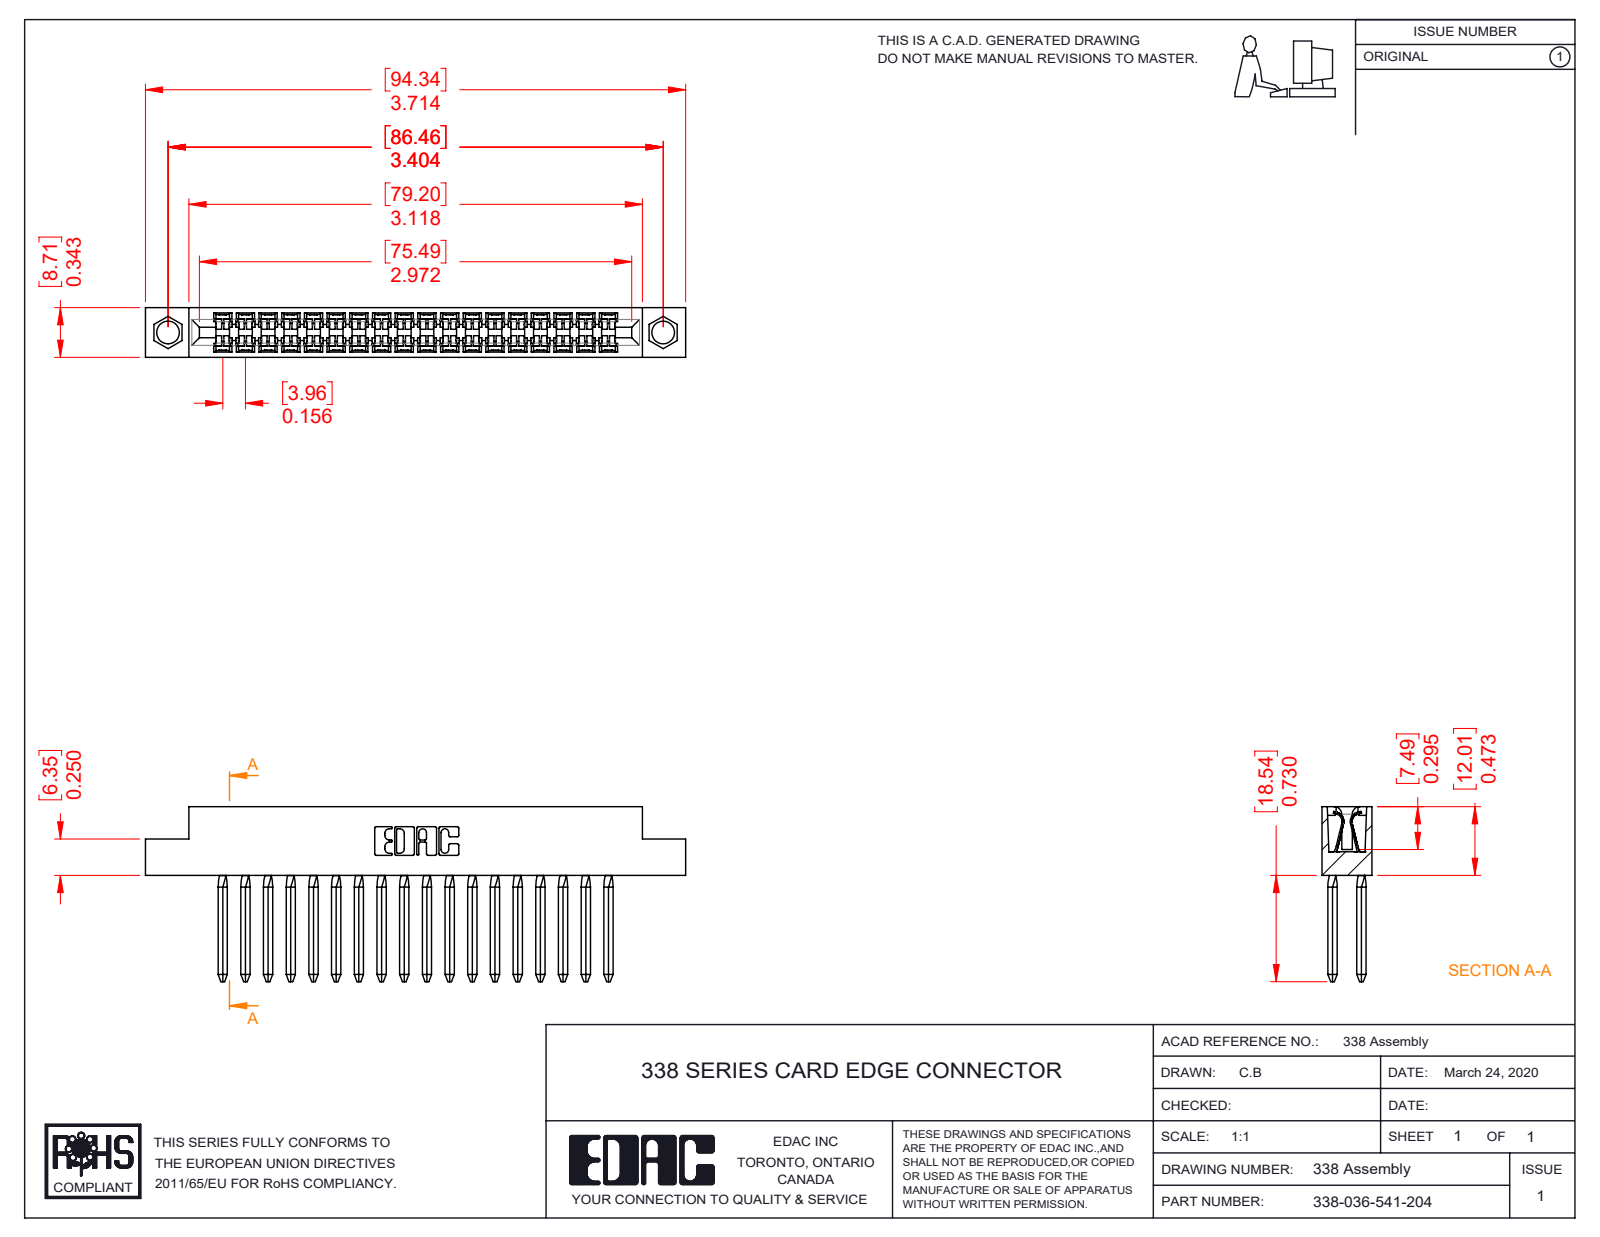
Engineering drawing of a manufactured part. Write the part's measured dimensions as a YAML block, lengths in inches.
part_name: "338-290-001_541; 338-210-001_338-210-018-004; 338-036-541-204"
step_written_by: "SolidWorks 2016 (CONFIG_CONTROL_DESIGN)"
units: inches
bodies: {solids: 37, faces: 2520, planar: 1756, cylindrical: 620, other: 144}
overall_size: [3.714, 1.203, 0.343]
volume: 0.433
surface_area: 19.81
round_holes:
  - {diameter: 0.156, count: 2}
partial_cylinders:
  - {radius: 0.025, count: 110}
  - {radius: 0.008, count: 36}
  - {radius: 0.055, count: 30}
  - {radius: 0.067, count: 30}
  - {radius: 0.1, count: 28}
  - {radius: 0.01, count: 22}
  - {radius: 0.007, count: 6}
  - {radius: 0.031, count: 6}
face_to_face_distances: [0.343, 0.156, 0.624, 0.11, 0.78, 0.468, 0.135, 0.207, 0.221, 0.312]
hole_center_spacings: [3.404]
